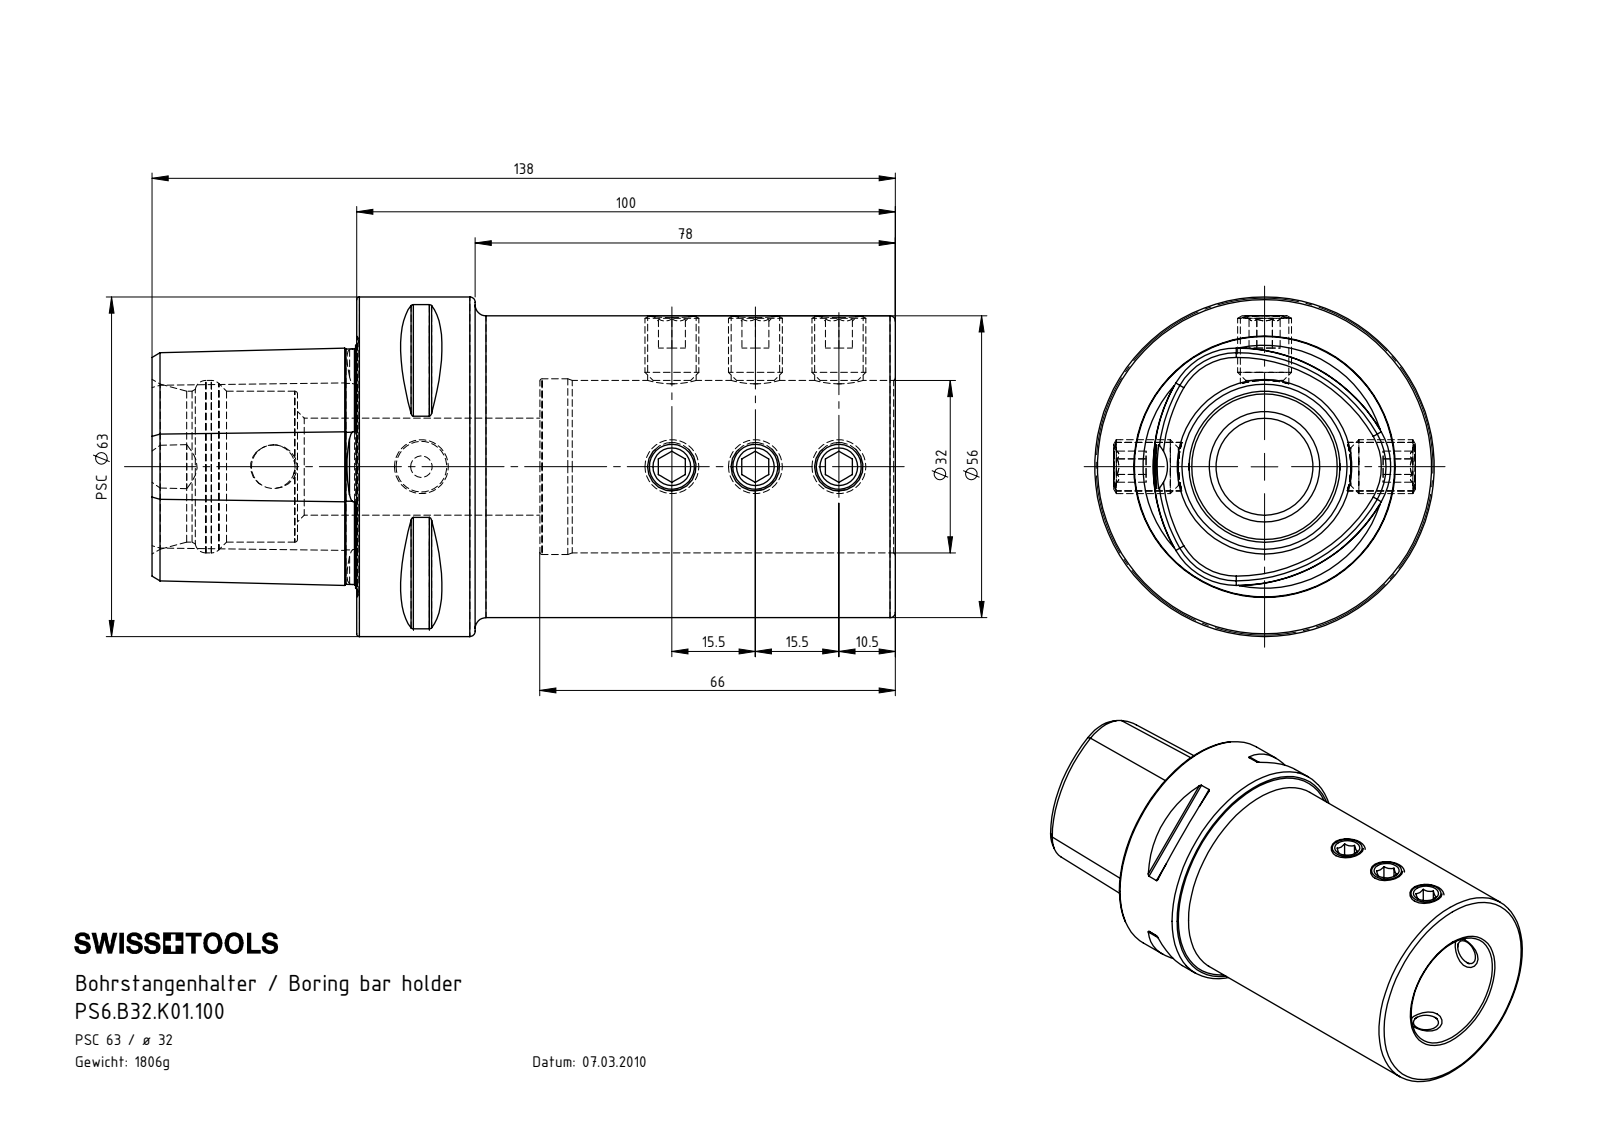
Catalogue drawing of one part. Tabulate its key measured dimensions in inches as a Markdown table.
| quantity | value |
| --- | --- |
| part name | ISO 4026 - M10 x 12_PreviewCfg; PS6-B32.K01.100_A; PS6.B32.K01.100 |
| STEP written by | SolidWorks 2017 (AUTOMOTIVE_DESIGN) |
| units | inches |
| bodies | 10 solids, 304 faces (102 planar, 67 cylindrical, 135 other) |
| overall size | 5.433 × 2.48 × 2.48 |
| volume | 14.06 in³ |
| surface area | 74.02 in² |
| round holes (diameter × count) | 0.354 × 6, 0.157 × 1, 0.319 × 1, 0.709 × 1, 1.102 × 1, 1.26 × 1, 1.283 × 1 |
| round bosses / shafts (diameter × count) | 0.394 × 6, 2.48 × 1, 2.205 × 1 |
| partial cylindrical surfaces (radius × count) | 0.02 × 8, 0.236 × 1 |
| main face-to-face distances | 3.937, 1.339, 1.496, 2.598, 2.835, 5.433, 0.197, 0.61, 0.305, 0.236 |
| hole center spacings | 0.61, 1.22, 1.083, 1.831, 2.441, 2.913, 3.051, 3.524 |
